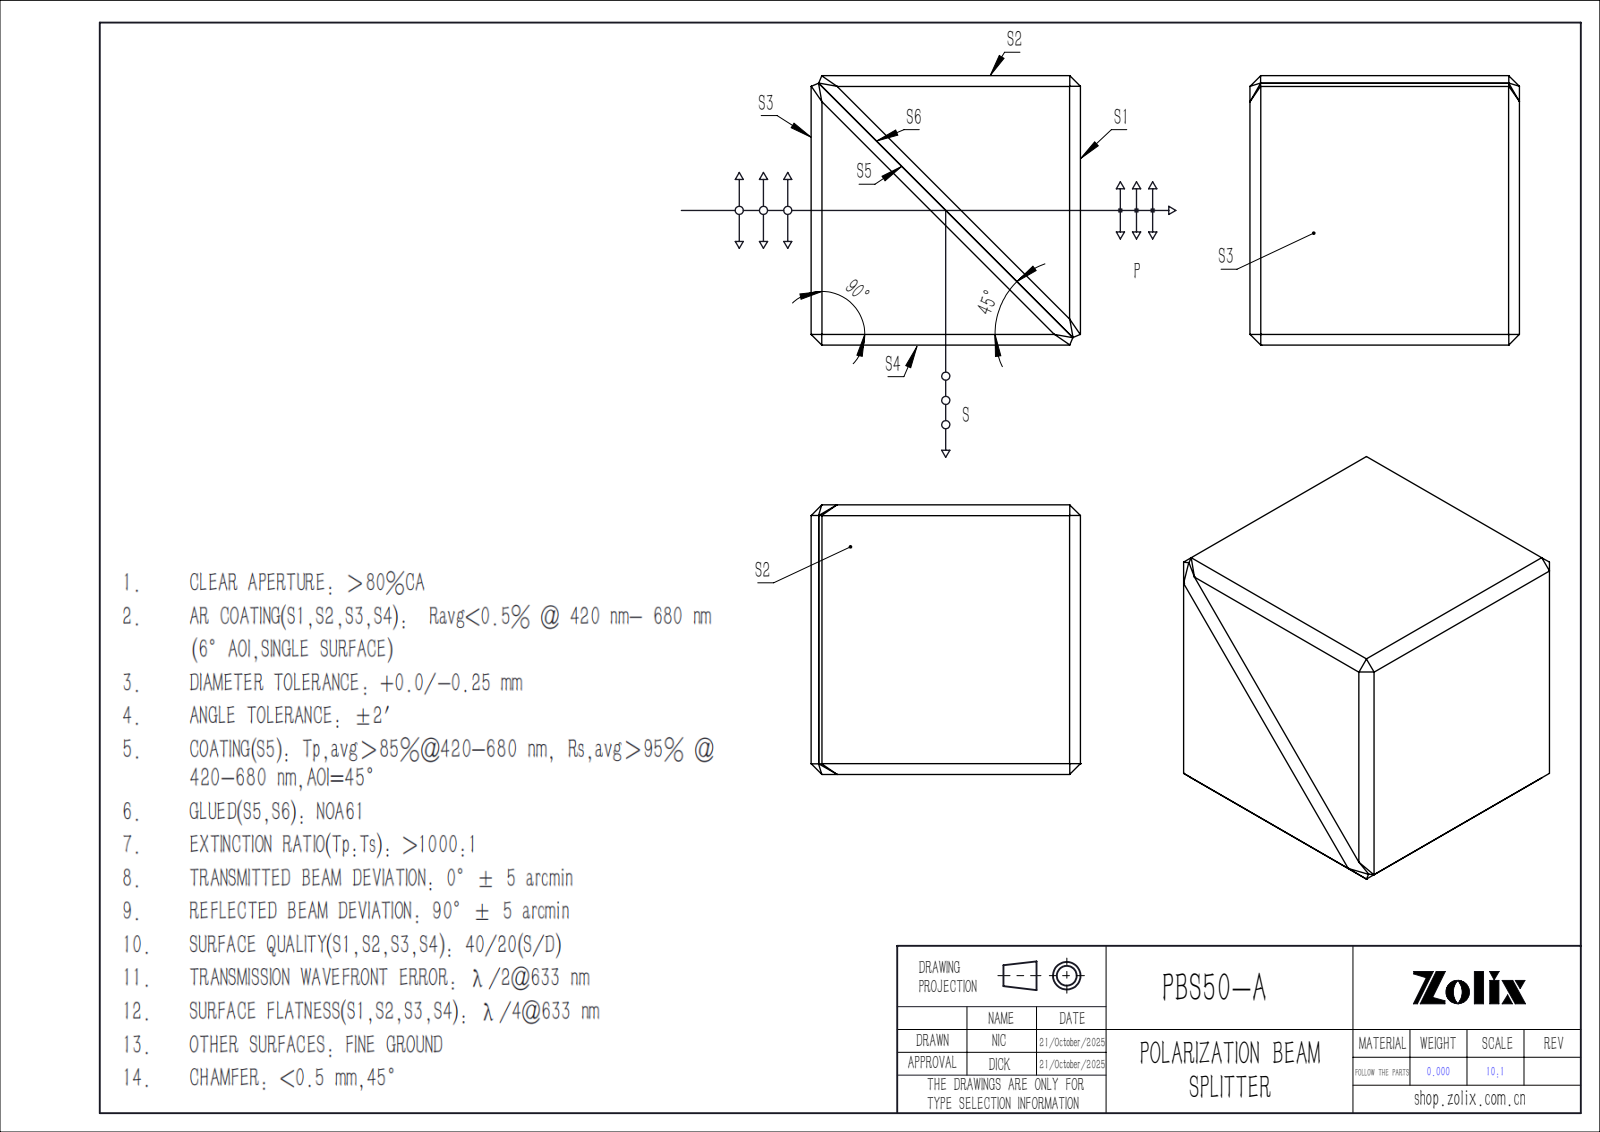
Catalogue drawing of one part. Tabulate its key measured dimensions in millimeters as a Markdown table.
| quantity | value |
| --- | --- |
| part name | PBS651 |
| STEP written by | SolidWorks 2022 (CONFIG_CONTROL_DESIGN) |
| units | millimeters |
| bodies | 2 solids, 43 faces (41 planar, 2 cylindrical, 0 other) |
| overall size | 50.8 × 50.8 × 50.8 |
| volume | 131 073 mm³ |
| surface area | 22 668 mm² |
| round holes (diameter × count) | 1.2 × 1 |
| main face-to-face distances | 50.8, 71.55, 35.64, 35.77, 71.54, 50.65, 50.66, 50.51, 45.8, 5 |
